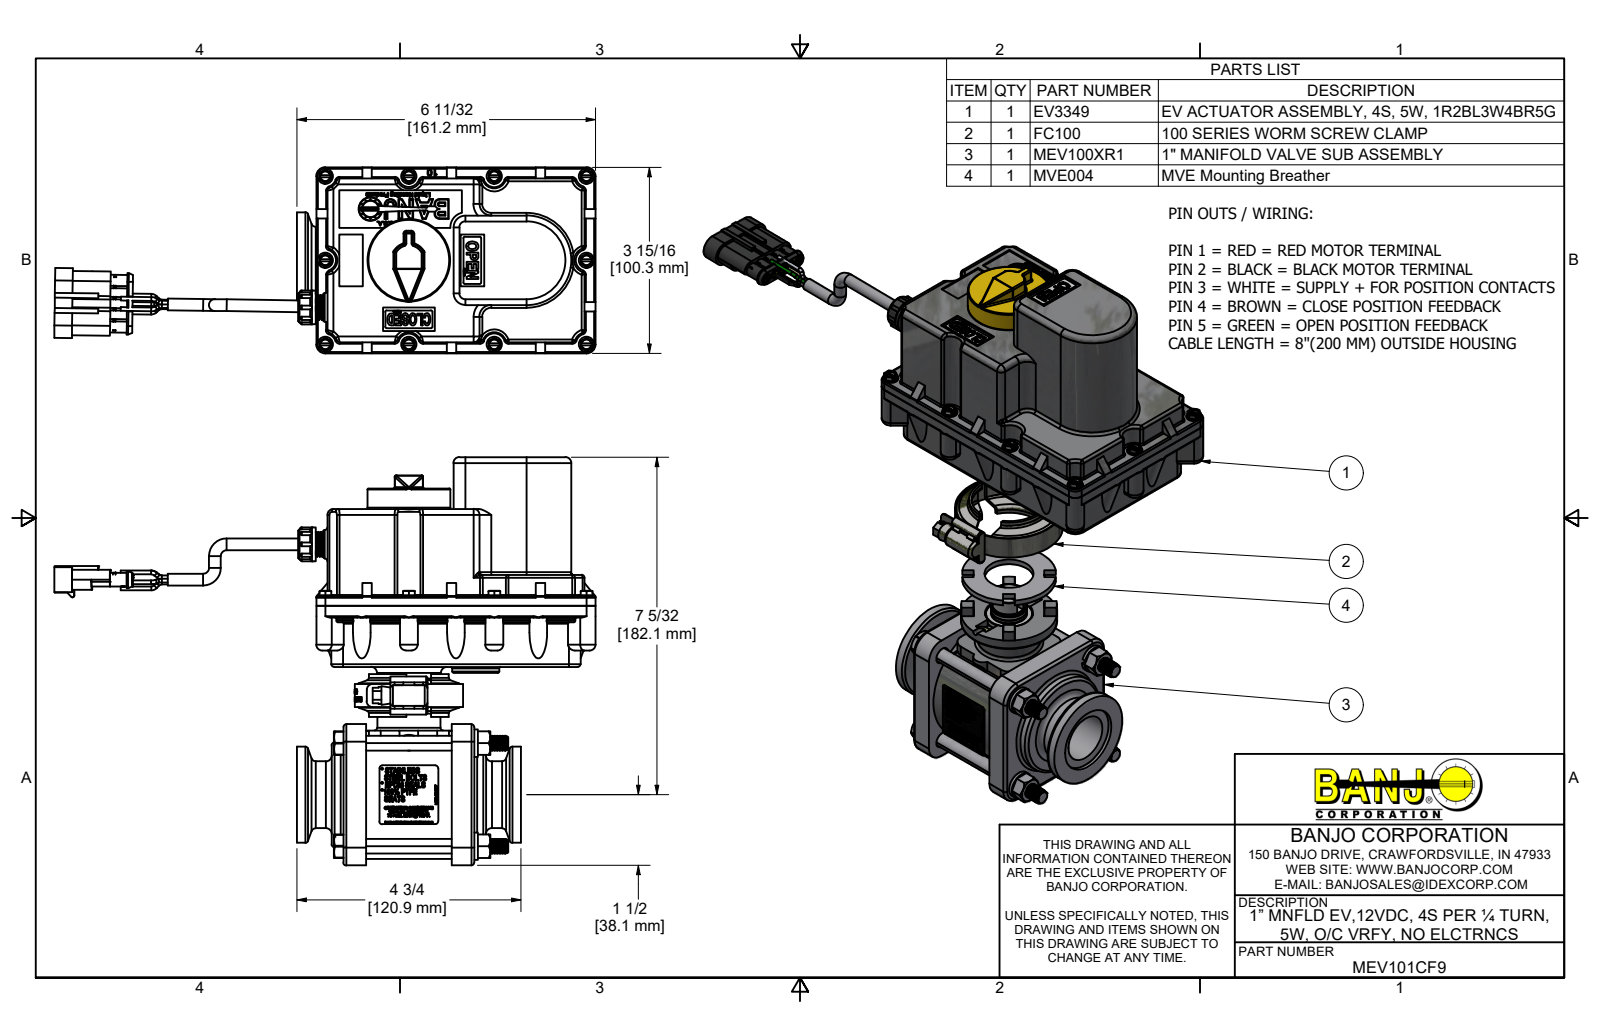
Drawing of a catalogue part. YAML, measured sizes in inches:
part_name: "MEV101CF9; MEV100XR1; MEV10254A; MEV10254AX (+8 more)"
step_written_by: "Autodesk Inventor 2022 (AUTOMOTIVE_DESIGN)"
units: inches
bodies: {solids: 77, faces: 8580, planar: 3785, cylindrical: 1896, other: 2899}
overall_size: [11.5, 8.668, 3.95]
volume: 55.88
surface_area: 617.9
round_holes:
  - {diameter: 0.16, count: 12}
  - {diameter: 0.11, count: 10}
  - {diameter: 0.2, count: 10}
  - {diameter: 0.12, count: 6}
  - {diameter: 0.15, count: 6}
  - {diameter: 0.176, count: 6}
  - {diameter: 0.055, count: 5}
  - {diameter: 0.217, count: 5}
  - {diameter: 0.252, count: 4}
  - {diameter: 0.322, count: 4}
  - {diameter: 0.36, count: 4}
  - {diameter: 0.1, count: 3}
round_bosses_or_shafts:
  - {diameter: 0.268, count: 60}
  - {diameter: 0.08, count: 19}
  - {diameter: 0.328, count: 10}
  - {diameter: 0.138, count: 10}
  - {diameter: 0.103, count: 8}
  - {diameter: 0.232, count: 5}
  - {diameter: 0.173, count: 5}
  - {diameter: 0.154, count: 5}
partial_cylinders:
  - {radius: 0.03, count: 132}
  - {radius: 0.06, count: 67}
  - {radius: 0.02, count: 63}
  - {radius: 0.125, count: 28}
  - {radius: 0.315, count: 24}
  - {radius: 0.5, count: 24}
  - {radius: 0.02, count: 21}
  - {radius: 0.007, count: 20}
face_to_face_distances: [0.125, 0.125, 2.3, 0.2, 1.1, 0.78, 0.25, 1.3, 3.23, 3.355]
hole_center_spacings: [1.68, 2.058, 1.684, 1.785, 2.376, 0.236, 0.492, 1.188]
